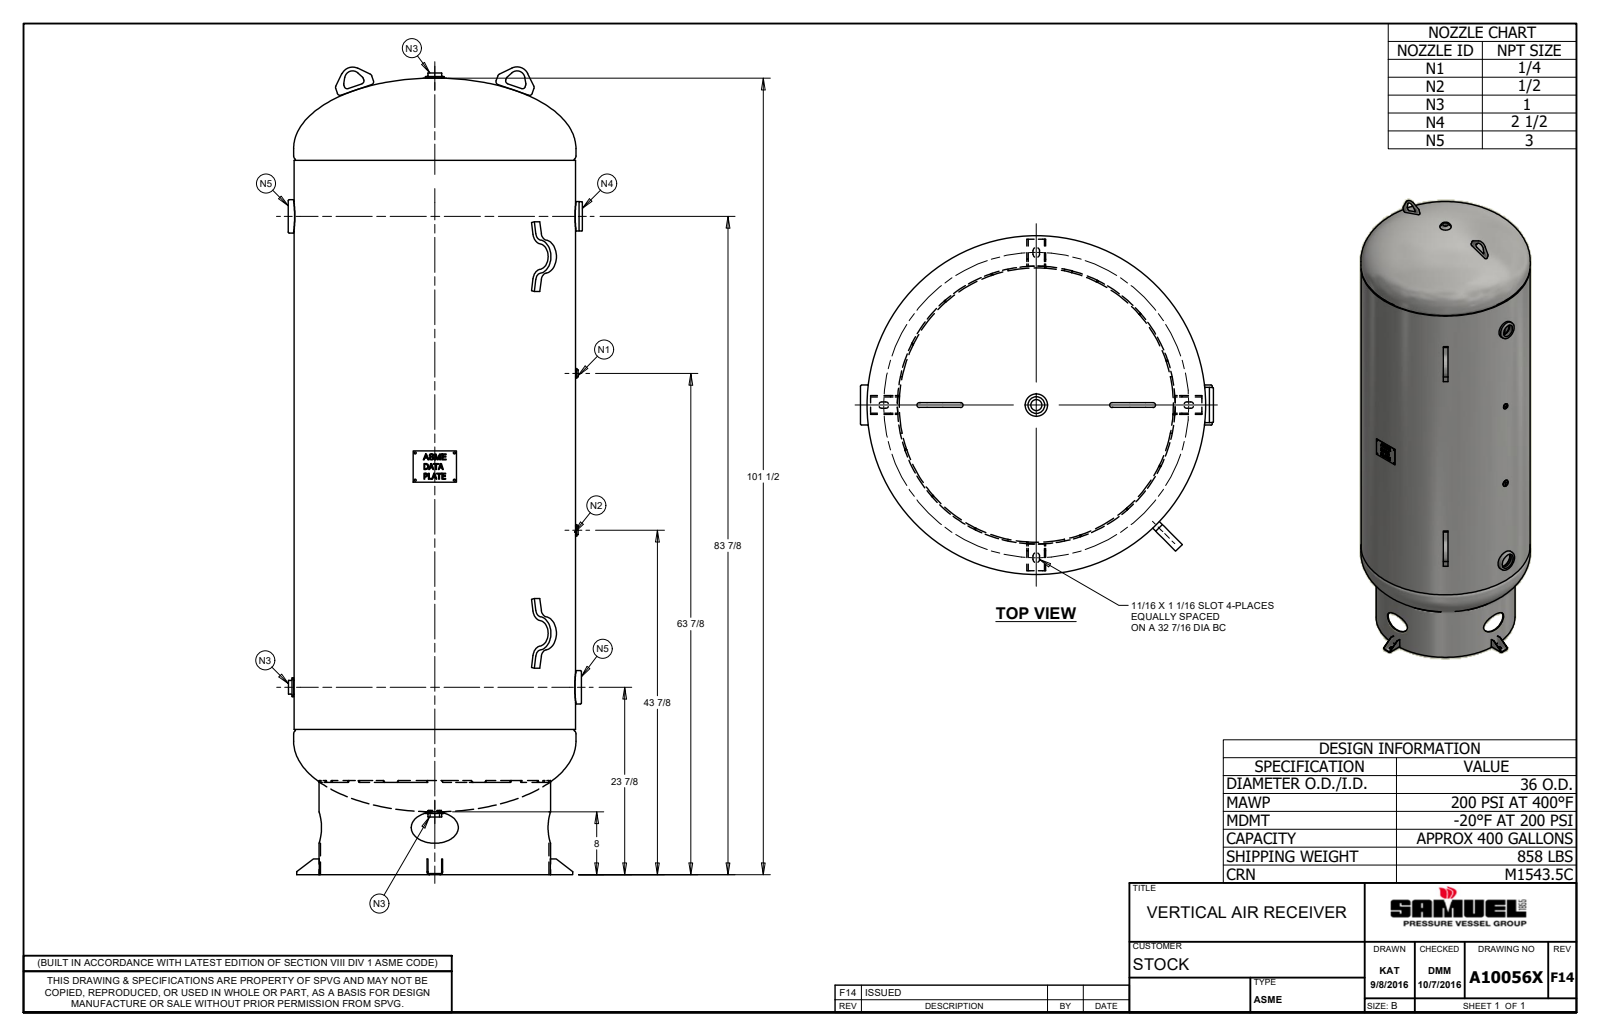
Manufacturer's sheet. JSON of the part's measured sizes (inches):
{"part_name": "A10056X; 37-2171; 37-2080; A10056X-2HD (+8 more)", "step_written_by": "Autodesk Inventor 2019 (CONFIG_CONTROL_DESIGN)", "units": "inches", "bodies": {"solids": 21, "faces": 515, "planar": 277, "cylindrical": 109, "other": 129}, "overall_size": [102.918, 37.5, 36], "volume_in3": 2660, "surface_area_in2": 25271, "round_holes": [[0.25, 4], [1.193, 2], [1.813, 2], [3.25, 2], [3.875, 2], [0.451, 1], [0.734, 1], [1.063, 1], [1.25, 1], [2.578, 1], [3.187, 1], [29.126, 1]], "round_bosses_or_shafts": [[4.25, 2], [3.813, 2], [2.375, 2], [1.75, 2], [1.703, 2], [0.5, 2], [35.9, 1], [29.5, 1]], "partial_cylinders_radius": [[0.25, 16], [0.344, 8], [0.187, 4], [0.322, 4], [1, 4], [1.5, 4], [7.37, 4], [1.625, 2]], "face_to_face_distances": [0.5, 72, 0.135, 19, 90.5, 71.5, 1, 1.865, 18.5, 91], "hole_center_spacings": [20, 40, 3.5, 5, 6.103, 20, 20, 40]}
